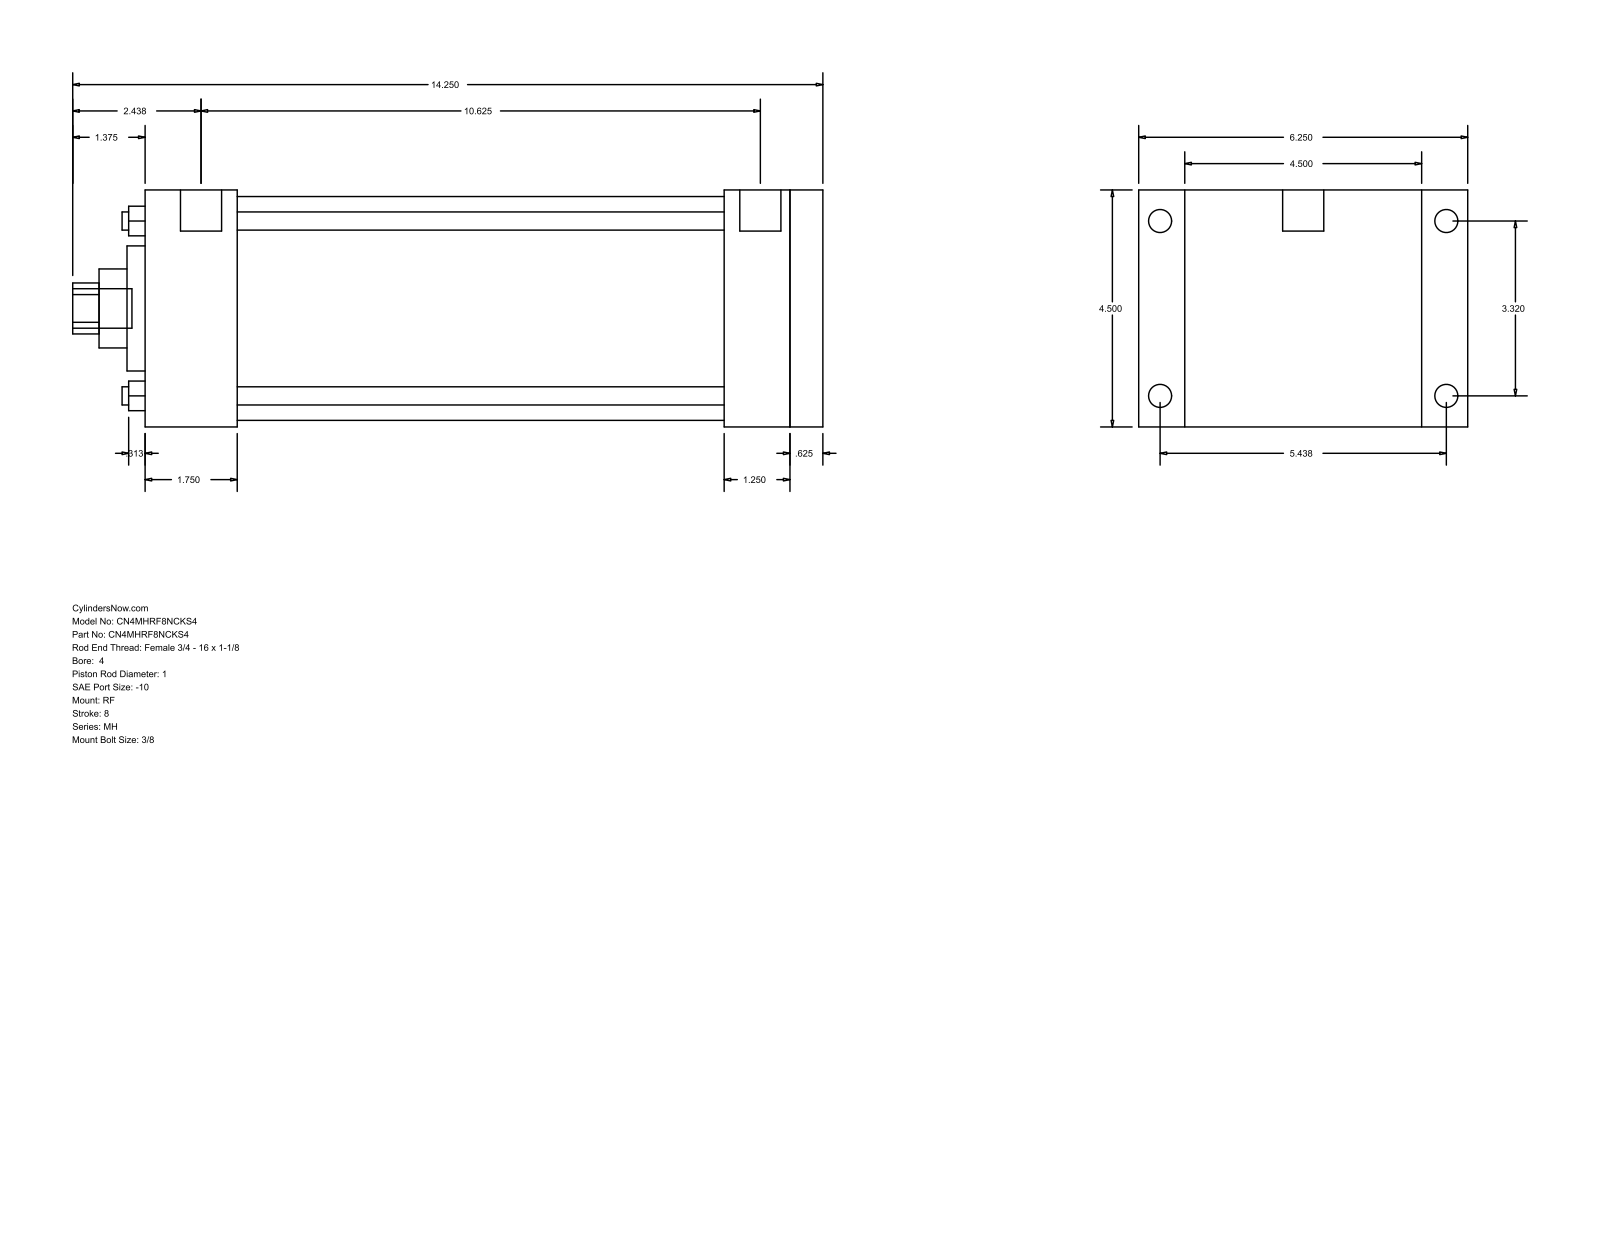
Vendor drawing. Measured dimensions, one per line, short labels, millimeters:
name: MH_RF__0400_1
written by: GSSL Pune (CONFIG_CONTROL_DESIGN)
unit: mm
bodies: 0 solids, 94 faces (65 planar, 29 cylindrical, 0 other)
size: 361.95 × 158.75 × 114.3
holes: 4× ⌀8.76, 1× ⌀25.4, 1× ⌀38.1, 1× ⌀60.33, 1× ⌀107.95
bosses: 4× ⌀11.13, 4× ⌀8.73, 2× ⌀19.84, 1× ⌀19.05
rounds: 1× R12.29
face distances: 114.3, 327.03, 311.15, 15.88, 47.63, 44.46, 266.69, 282.57, 279.4, 234.94
hole spacings: 59.62, 84.32, 119.25
